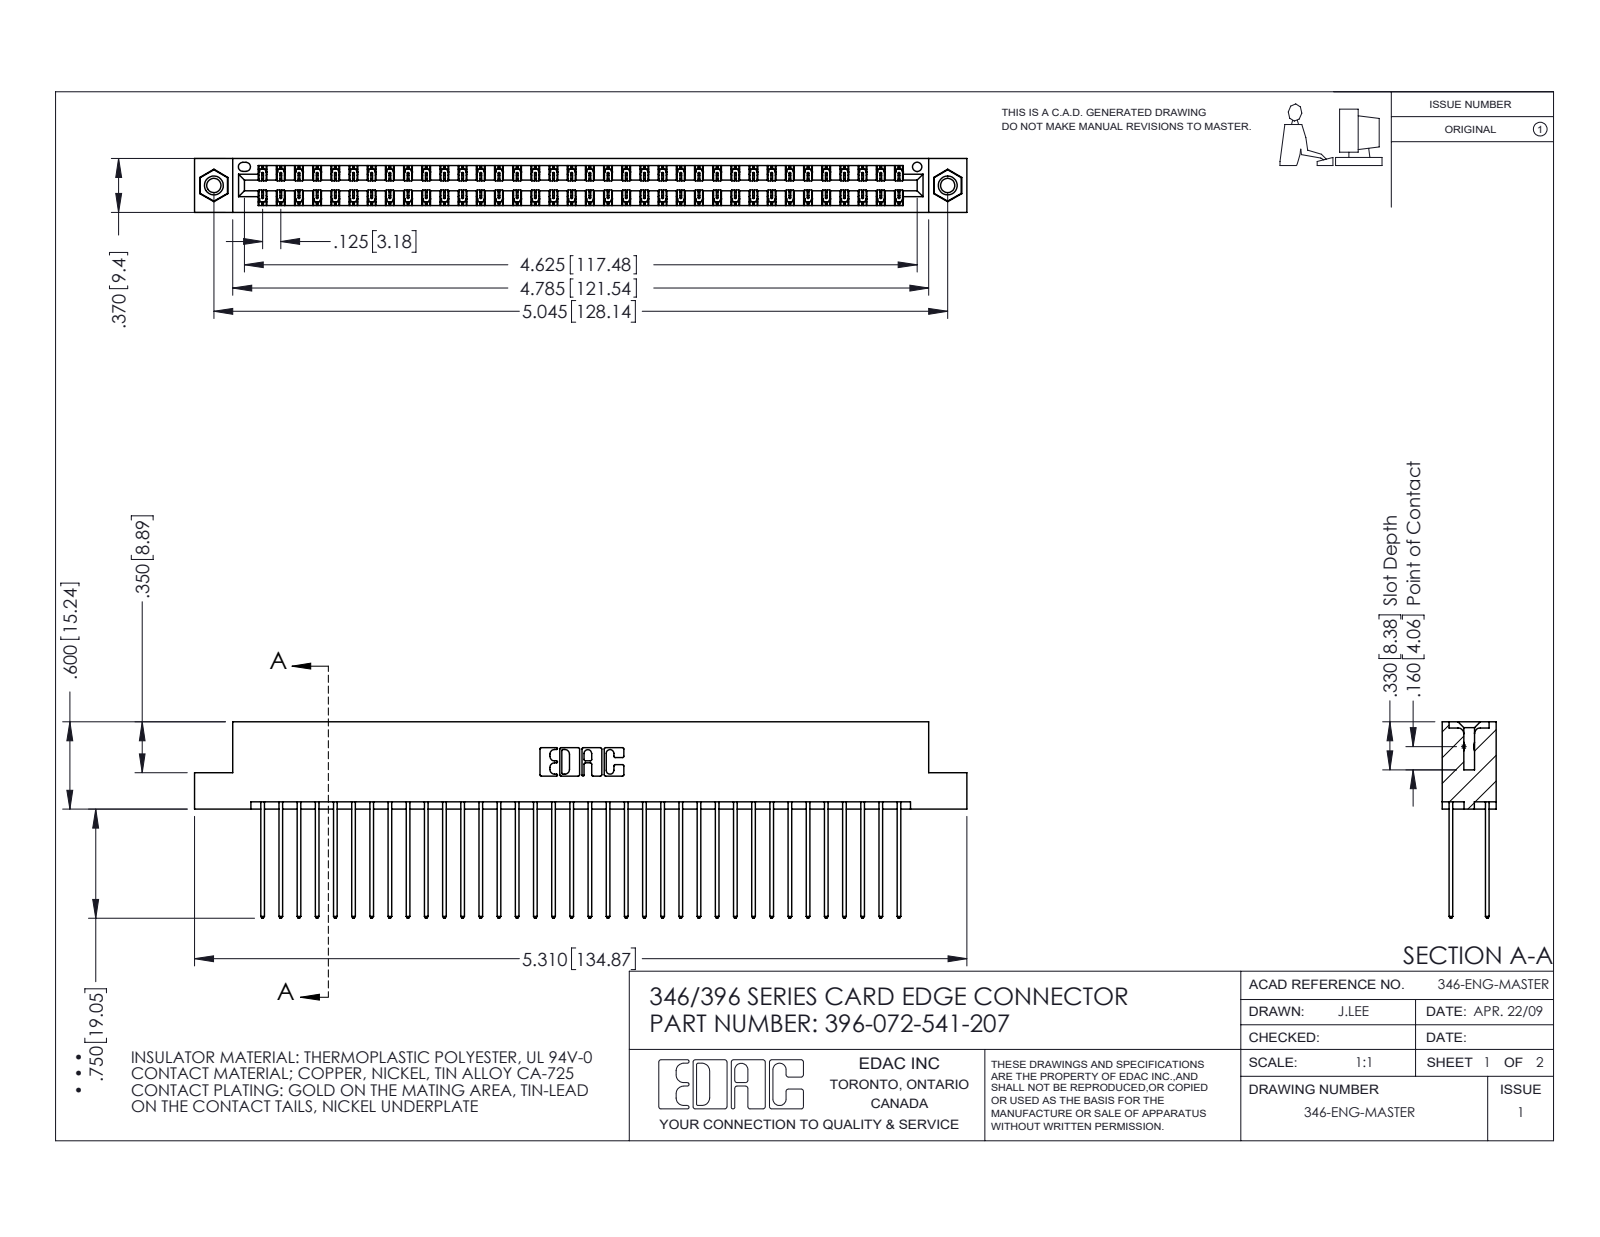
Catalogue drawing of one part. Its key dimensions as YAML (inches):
part_name: "346 Part_Flush Mounting Lugs - 0.156 Dia-TI; 396-072-541-207; 345-250-001_345-250-005-103; 345-292-001_345-293-141"
step_written_by: "SolidWorks 2016 (CONFIG_CONTROL_DESIGN)"
units: inches
bodies: {solids: 75, faces: 3926, planar: 2628, cylindrical: 1282, other: 16}
overall_size: [5.31, 1.35, 0.37]
volume: 0.824
surface_area: 31.75
round_holes:
  - {diameter: 0.098, count: 2}
  - {diameter: 0.125, count: 2}
  - {diameter: 0.156, count: 2}
  - {diameter: 0.064, count: 1}
round_bosses_or_shafts:
  - {diameter: 0.155, count: 2}
partial_cylinders:
  - {radius: 0.006, count: 108}
  - {radius: 0.01, count: 72}
  - {radius: 0.01, count: 22}
  - {radius: 0.007, count: 6}
  - {radius: 0.031, count: 6}
  - {radius: 0.026, count: 3}
  - {radius: 0.014, count: 2}
  - {radius: 0.022, count: 2}
face_to_face_distances: [0.048, 0.322, 0.25, 0.072, 0.298, 0.025, 0.37, 0.275, 0.225, 0.148]
hole_center_spacings: [0.246, 4.836, 5.045]
